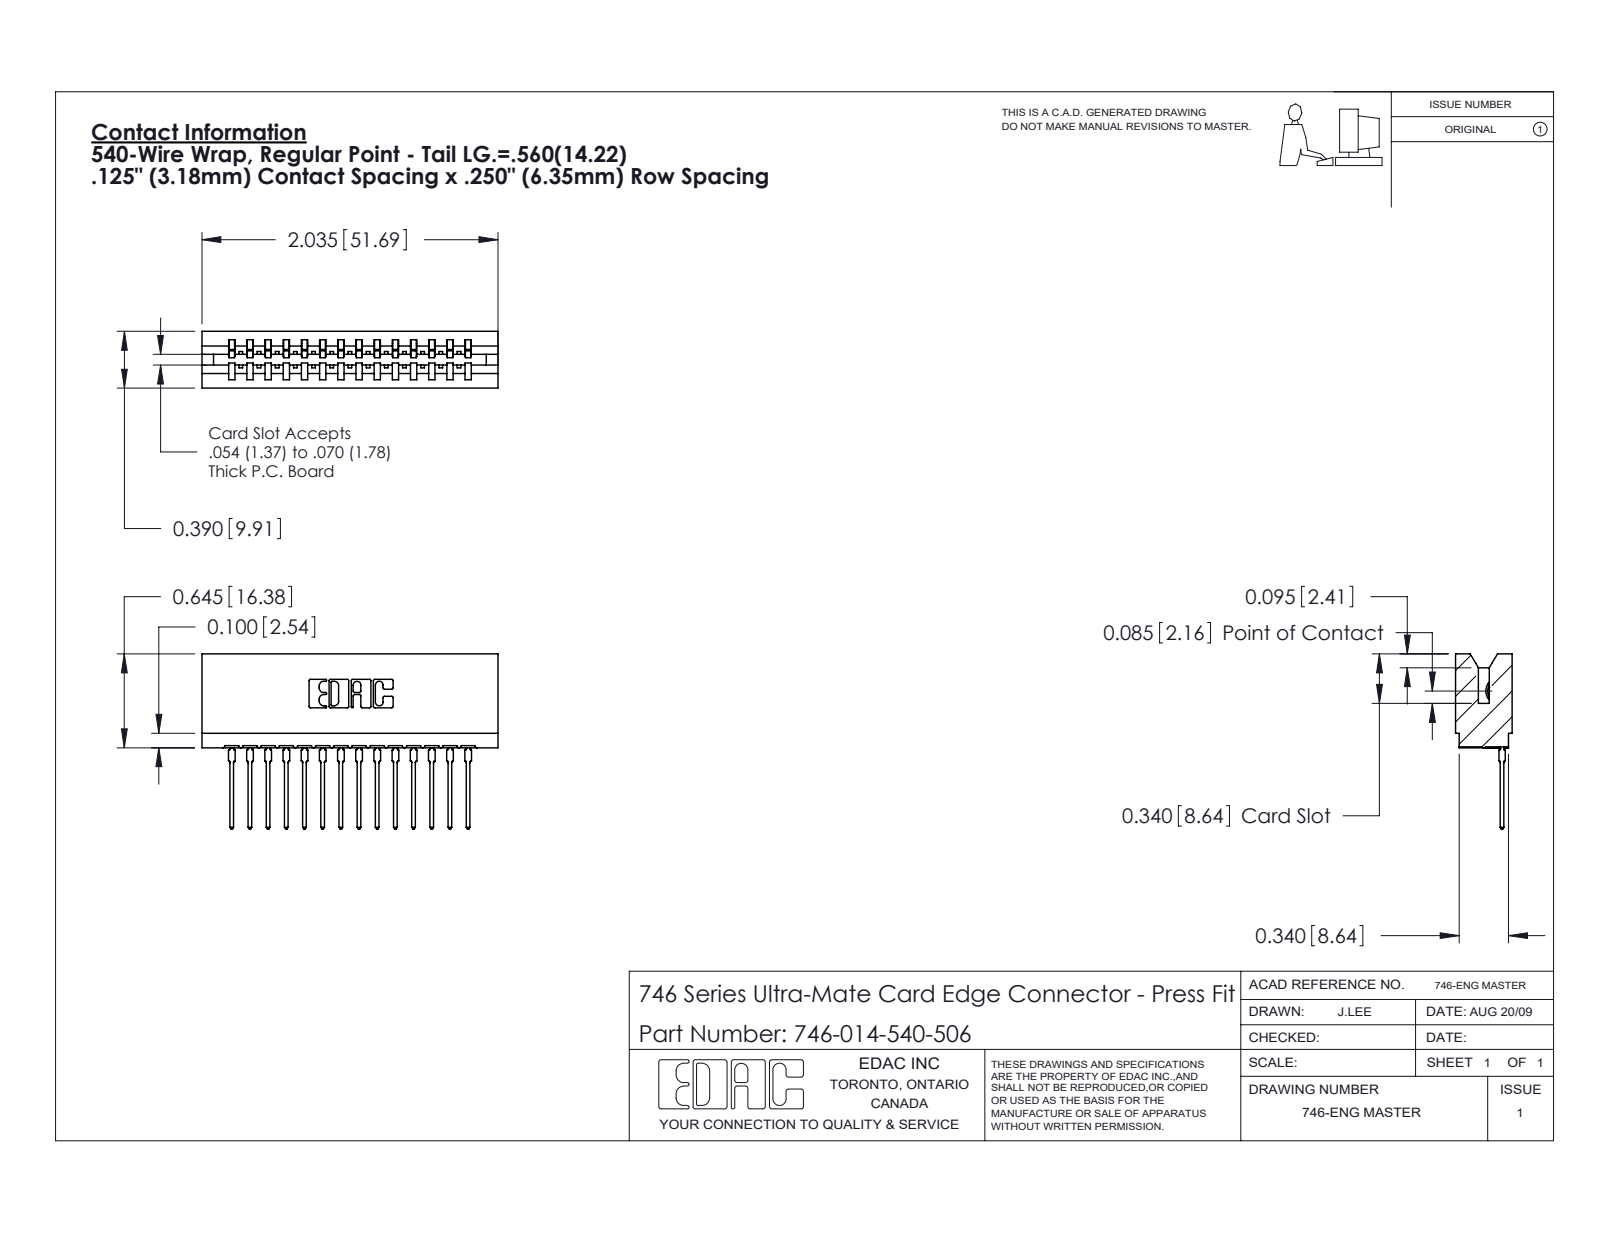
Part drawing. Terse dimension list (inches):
name: 746-292-001_540; 746 Part_.340 Slot Depth - 06; 746-014-540-506
written by: SolidWorks 2020 (CONFIG_CONTROL_DESIGN)
unit: in
bodies: 15 solids, 1610 faces (938 planar, 308 cylindrical, 364 other)
size: 2.035 × 1.204 × 0.39
volume: 0.365 in³; area: 12.13 in²
rounds: 28× R0.021, 22× R0.01, 15× R0.015, 6× R0.007, 6× R0.031, 4× R0.005, 4× R0.011, 3× R0.026
face distances: 0.25, 0.333, 0.057, 0.5, 0.39, 0.042, 0.125, 0.75, 0.125, 0.292
